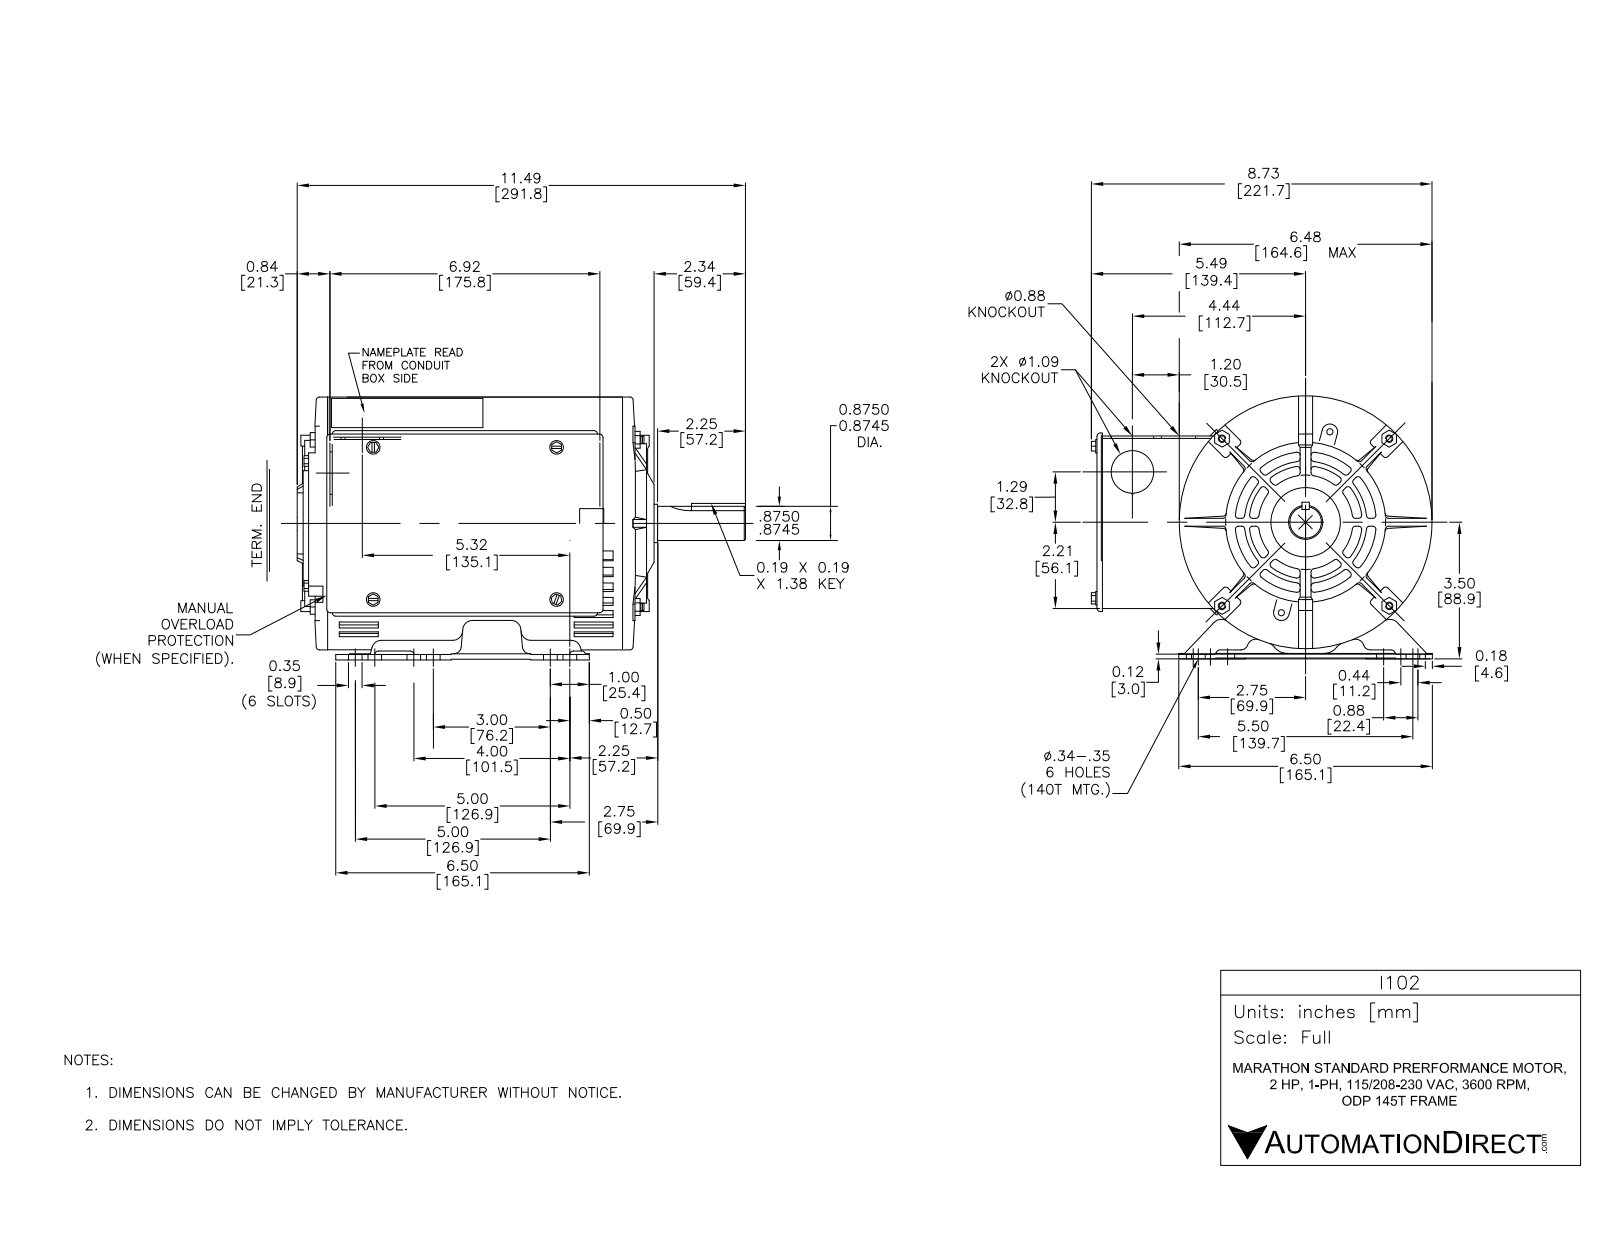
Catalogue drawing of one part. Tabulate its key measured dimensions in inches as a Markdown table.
| quantity | value |
| --- | --- |
| part name | 100119-756 |
| STEP written by | SolidWorks 2015 (CONFIG_CONTROL_DESIGN) |
| units | inches |
| bodies | 26 solids, 3500 faces (1391 planar, 709 cylindrical, 1400 other) |
| overall size | 11.679 × 8.797 × 6.716 |
| volume | 45.73 in³ |
| surface area | 891.6 in² |
| round holes (diameter × count) | 0.22 × 8, 0.31 × 8, 0.345 × 6, 0.153 × 5, 0.145 × 4, 0.15 × 4, 0.188 × 4, 0.193 × 4, 0.25 × 4, 0.125 × 2, 0.144 × 2, 0.504 × 2 |
| round bosses / shafts (diameter × count) | 0.164 × 6, 0.399 × 4, 0.335 × 4, 0.19 × 4, 0.166 × 4, 0.34 × 2, 0.335 × 2, 6.436 × 1 |
| partial cylindrical surfaces (radius × count) | 0.06 × 55, 0.25 × 36, 0.08 × 30, 0.05 × 28, 0.02 × 21, 0.03 × 21, 0.09 × 21, 0.1 × 16 |
| main face-to-face distances | 0.06, 4.36, 0.044, 6.93, 4.42, 4.3, 0.119, 1.263, 1.323, 5.623 |
| hole center spacings | 4.283, 0.035, 3.027, 3.03, 3.9, 4.28, 4.285, 4.7 |
